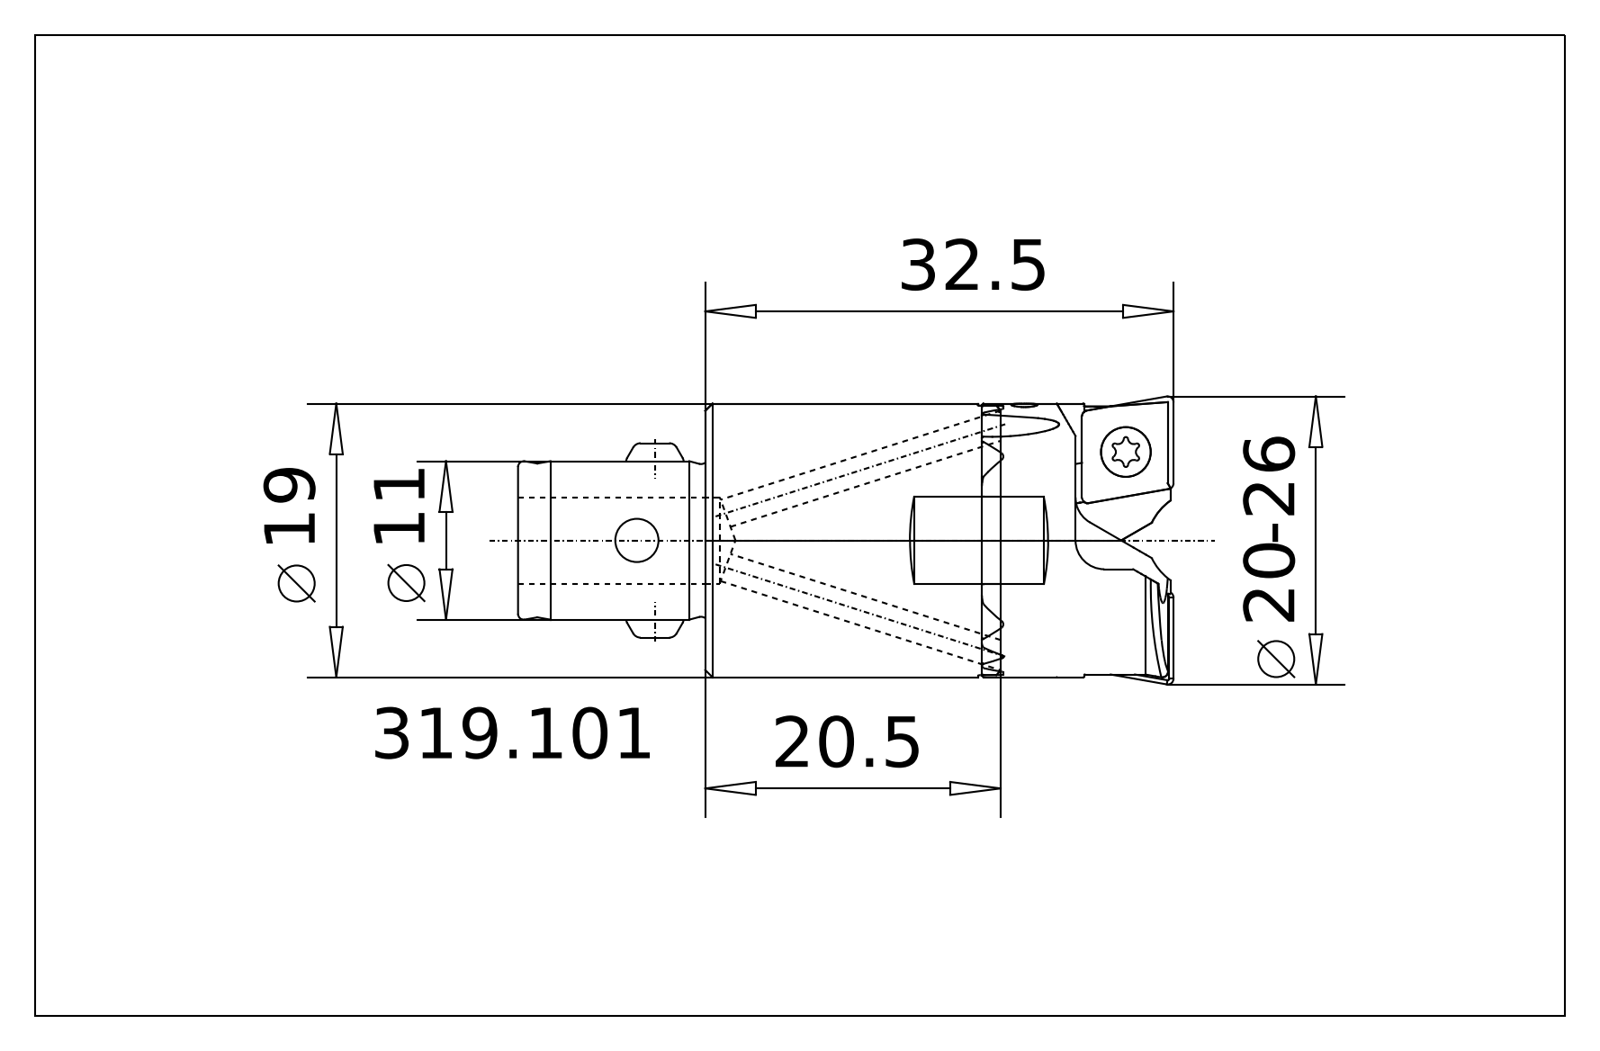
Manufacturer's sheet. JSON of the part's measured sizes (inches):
{"part_name": "319.101 Kaiser SW20-26(31)xCK1|690.191 Kaiser ETL M1.6x0.25x7 spez;Linear austragen1; 319.101 Kaiser SW20-26(31)xCK1|319.150 Kaiser ETL SW20;Fase6; 319.101 Kaiser SW20-26(31)xCK1|690.188 Kaiser ETL M4x18;Verrundung2; 319.101 Kaiser SW20-26(31)xCK1|690.184 Kaiser ETL M1.6x8;Schnitt-Linear austragen2 (+3 more)", "step_written_by": "ACIS (automotive_design)", "units": "inches", "bodies": {"solids": 11, "faces": 641, "planar": 225, "cylindrical": 150, "other": 266}, "overall_size": [1.697, 0.748, 0.748], "volume_in3": 0.41, "surface_area_in2": 7.552, "round_holes": [[0.049, 3], [0.071, 3], [0.157, 3], [0.059, 2], [0.079, 2], [0.13, 2], [0.165, 2], [0.063, 1], [0.118, 1], [0.138, 1], [0.236, 1]], "round_bosses_or_shafts": [[0.276, 2], [0.098, 2], [0.063, 2], [0.748, 1], [0.433, 1], [0.155, 1], [0.118, 1], [0.091, 1]], "partial_cylinders_radius": [[0.008, 20], [0.004, 4], [0.079, 4], [0.049, 2], [0.059, 2], [0.067, 2], [0.087, 2], [0.374, 1]], "face_to_face_distances": [0.512, 0.087, 0.157, 0.128, 0.118, 0.447, 0.197, 0.738, 1.25, 0.089], "hole_center_spacings": [0.207, 0.098, 0.415, 1.011, 1.015]}
